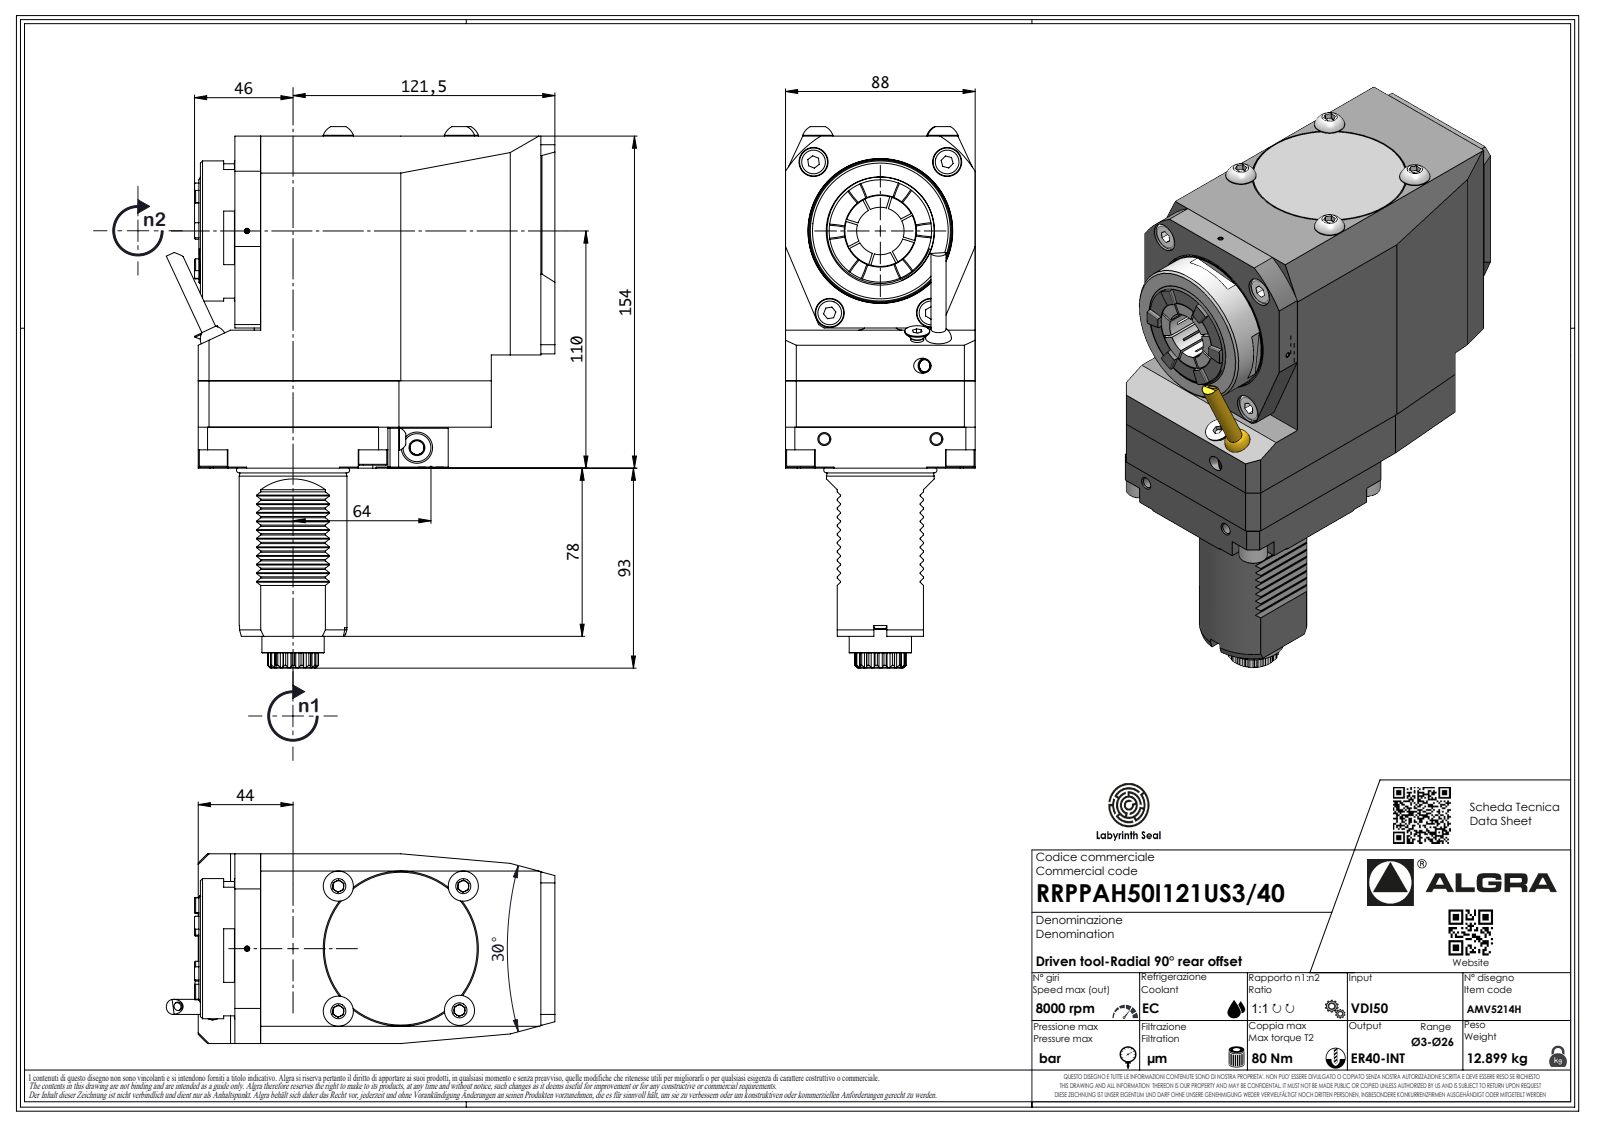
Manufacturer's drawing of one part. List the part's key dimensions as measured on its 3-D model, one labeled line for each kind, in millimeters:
Part name (STEP PRODUCT): RRPPAH50I121US340
STEP written by: SolidWorks 2023 (AUTOMOTIVE_DESIGN)
Units: millimetres
Bodies: 4 solids, 740 faces (446 planar, 151 cylindrical, 143 other)
Overall size (bounding box): 246.75 × 180.32 × 88
Volume: 2 020 000 mm³ · Surface area: 132 336 mm²
Round holes (diameter × count): ⌀2.1 ×1, ⌀36 ×1
Round bosses / shafts (diameter × count): ⌀72.66 ×1, ⌀65 ×1, ⌀50 ×1, ⌀48.7 ×1, ⌀28.9 ×1, ⌀20.8 ×1, ⌀7 ×1, ⌀6.37 ×1
Partial cylindrical surfaces — rounded edges, fillets, slot ends (radius × count): R1.61 ×36, R0.3 ×22, R0.33 ×7, R0.52 ×7, R3.7 ×7, R50.03 ×6, R6.75 ×4, R4 ×2
Main face-to-face distances: 88, 135, 154, 165.5, 1, 19, 17, 148.5, 64, 119
